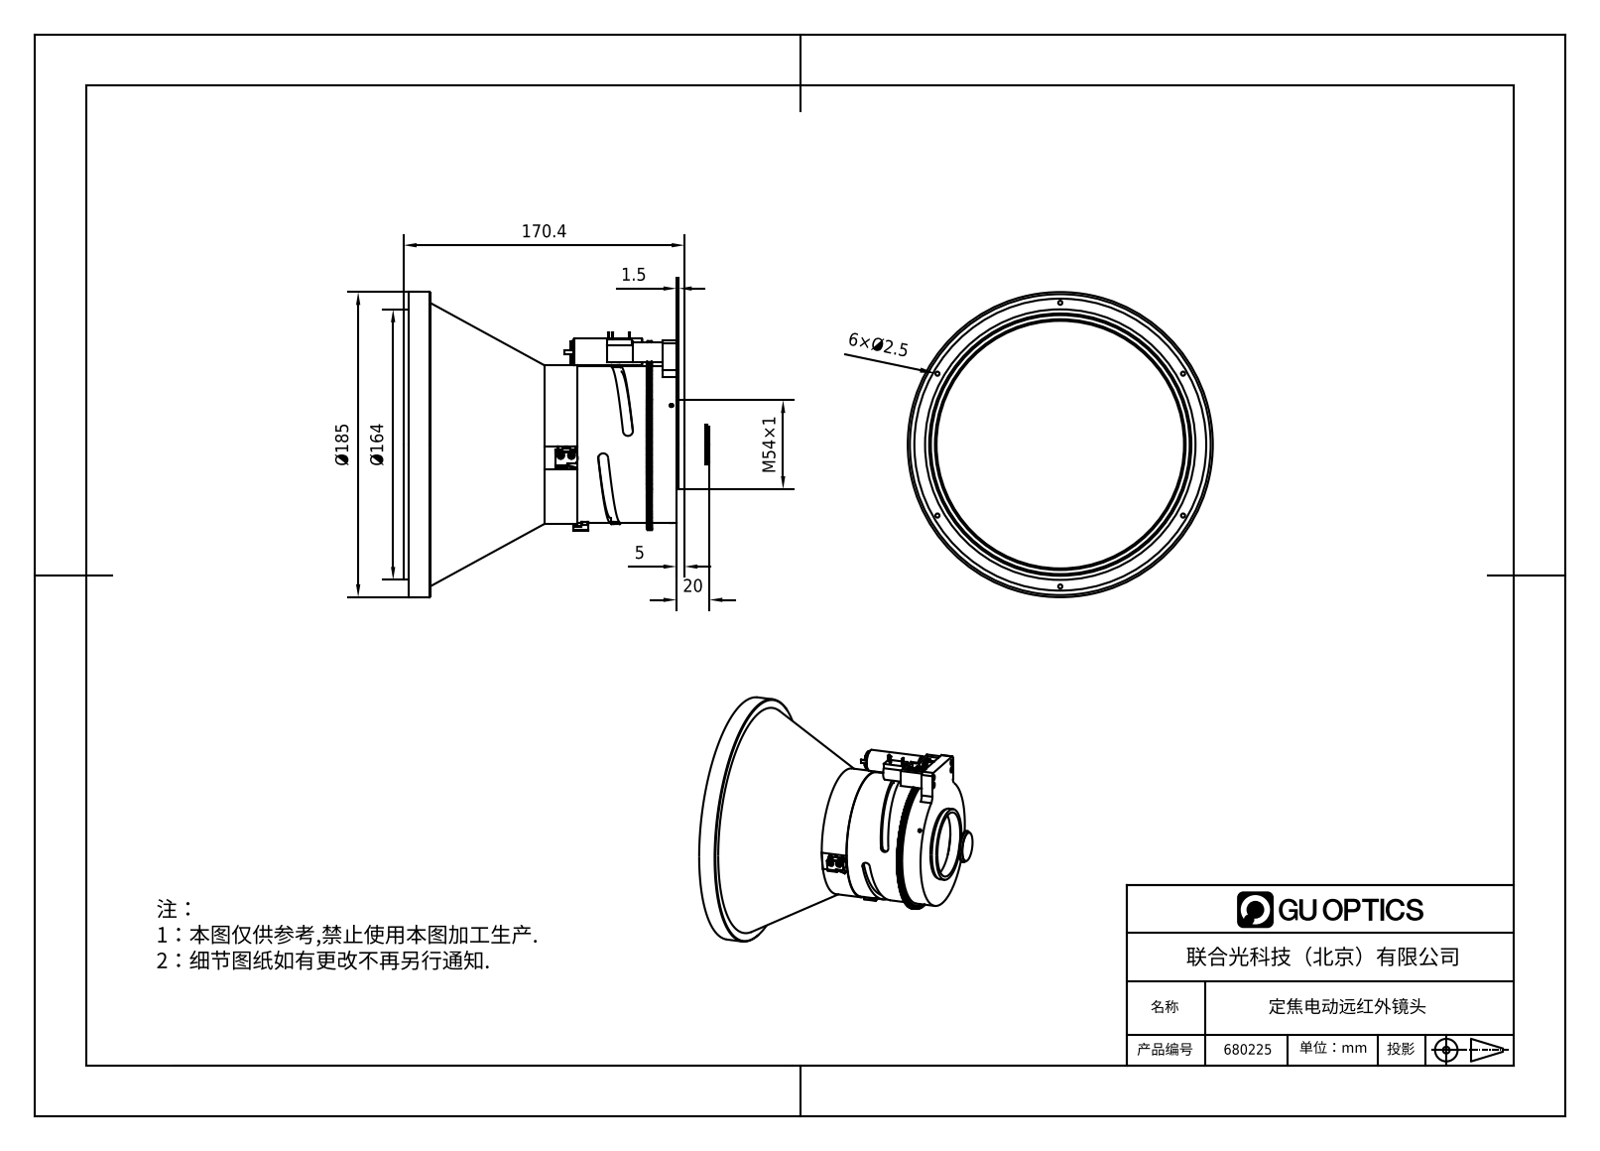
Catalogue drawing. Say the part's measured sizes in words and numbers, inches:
The part is named "LB-0044-3150F1电动调焦镜头外形图". Its 3-D file was written by "SolidWorks 2020 (CONFIG_CONTROL_DESIGN)". It is 47 solids with 3814 faces: 821 planar, 2241 cylindrical and 752 other. Overall it measures 7.302 by 7.283 by 7.283 inches. Its volume is 102.5 cubic inches and its surface area 244.8 square inches. Round holes: 12 of diameter 0.063, 12 of diameter 0.094, 6 of diameter 0.098, 5 of diameter 0.081, 4 of diameter 0.079, 4 of diameter 0.169, 3 of diameter 0.118, 1 of diameter 0.157, 1 of diameter 0.24, 1 of diameter 0.276, 1 of diameter 0.315, 1 of diameter 1.929. Round bosses or shafts: 10 of diameter 0.079, 8 of diameter 0.15, 8 of diameter 0.068, 7 of diameter 0.118, 6 of diameter 0.063, 6 of diameter 0.055, 5 of diameter 0.098, 4 of diameter 0.157. Partial cylindrical surfaces (rounded edges, fillets, slot ends): 1008 of radius 0.005, 408 of radius 0.072, 96 of radius 0.129, 12 of radius 0.02, 12 of radius 0.039, 8 of radius 0.079, 2 of radius 0.022, 2 of radius 0.024. The main face-to-face distances are 0.118, 6.392, 0.585, 0.512, 5.807, 6.274, 5.762, 5.88, 5.689, 5.177. The hole center spacings are 3.386, 0.256, 5.865, 0.315, 6.772, 0.199, 0.217, 0.236.
